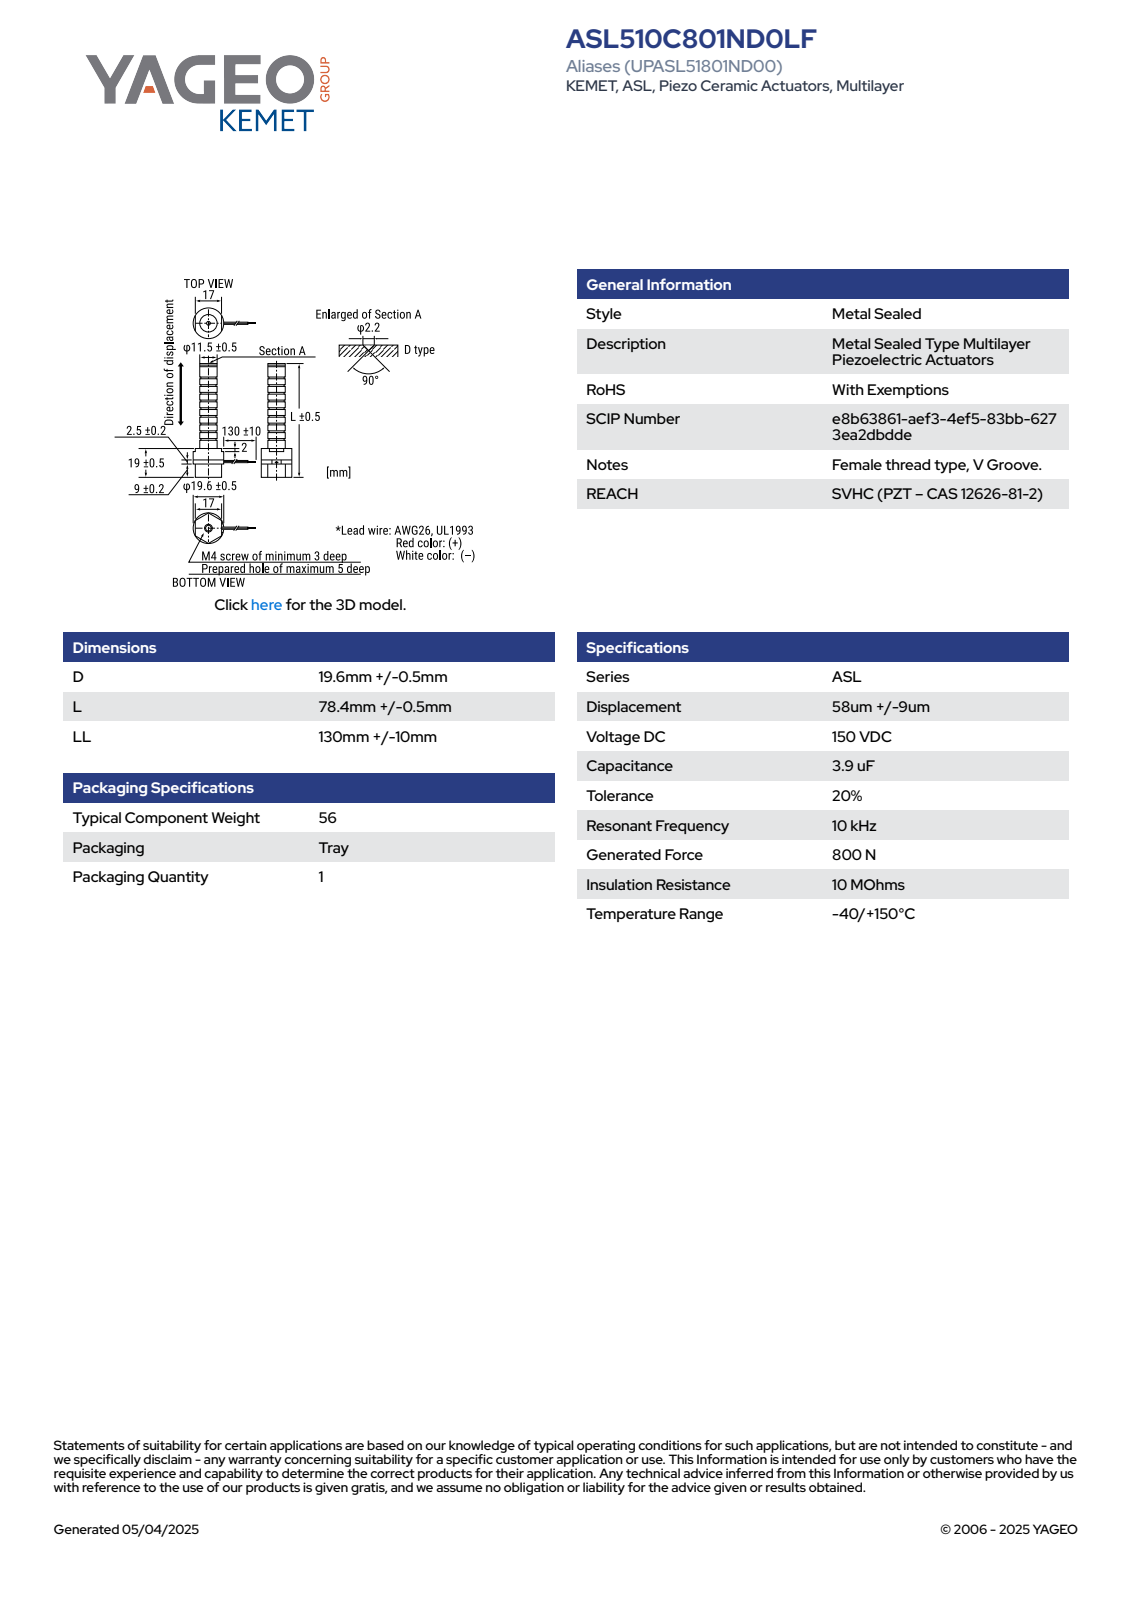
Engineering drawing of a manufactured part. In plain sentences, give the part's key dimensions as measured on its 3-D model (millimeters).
The part is named "AL_TPFE_D20.1L78.9". Its 3-D file was written by "SolidWorks 2014 (AUTOMOTIVE_DESIGN)". It is 2 solids with 122 faces: 70 planar, 20 cylindrical and 32 other. Overall it measures 84.91 by 20.1 by 20.1 millimeters. Its volume is 12 730 cubic millimeters and its surface area 4 718 square millimeters. Round bosses or shafts: 1 of diameter 20.1, 1 of diameter 12. The main face-to-face distances are 19.5, 17.24, 17, 84.9, 65.4, 9.2, 10.3, 75.7, 17.5, 8.3.
